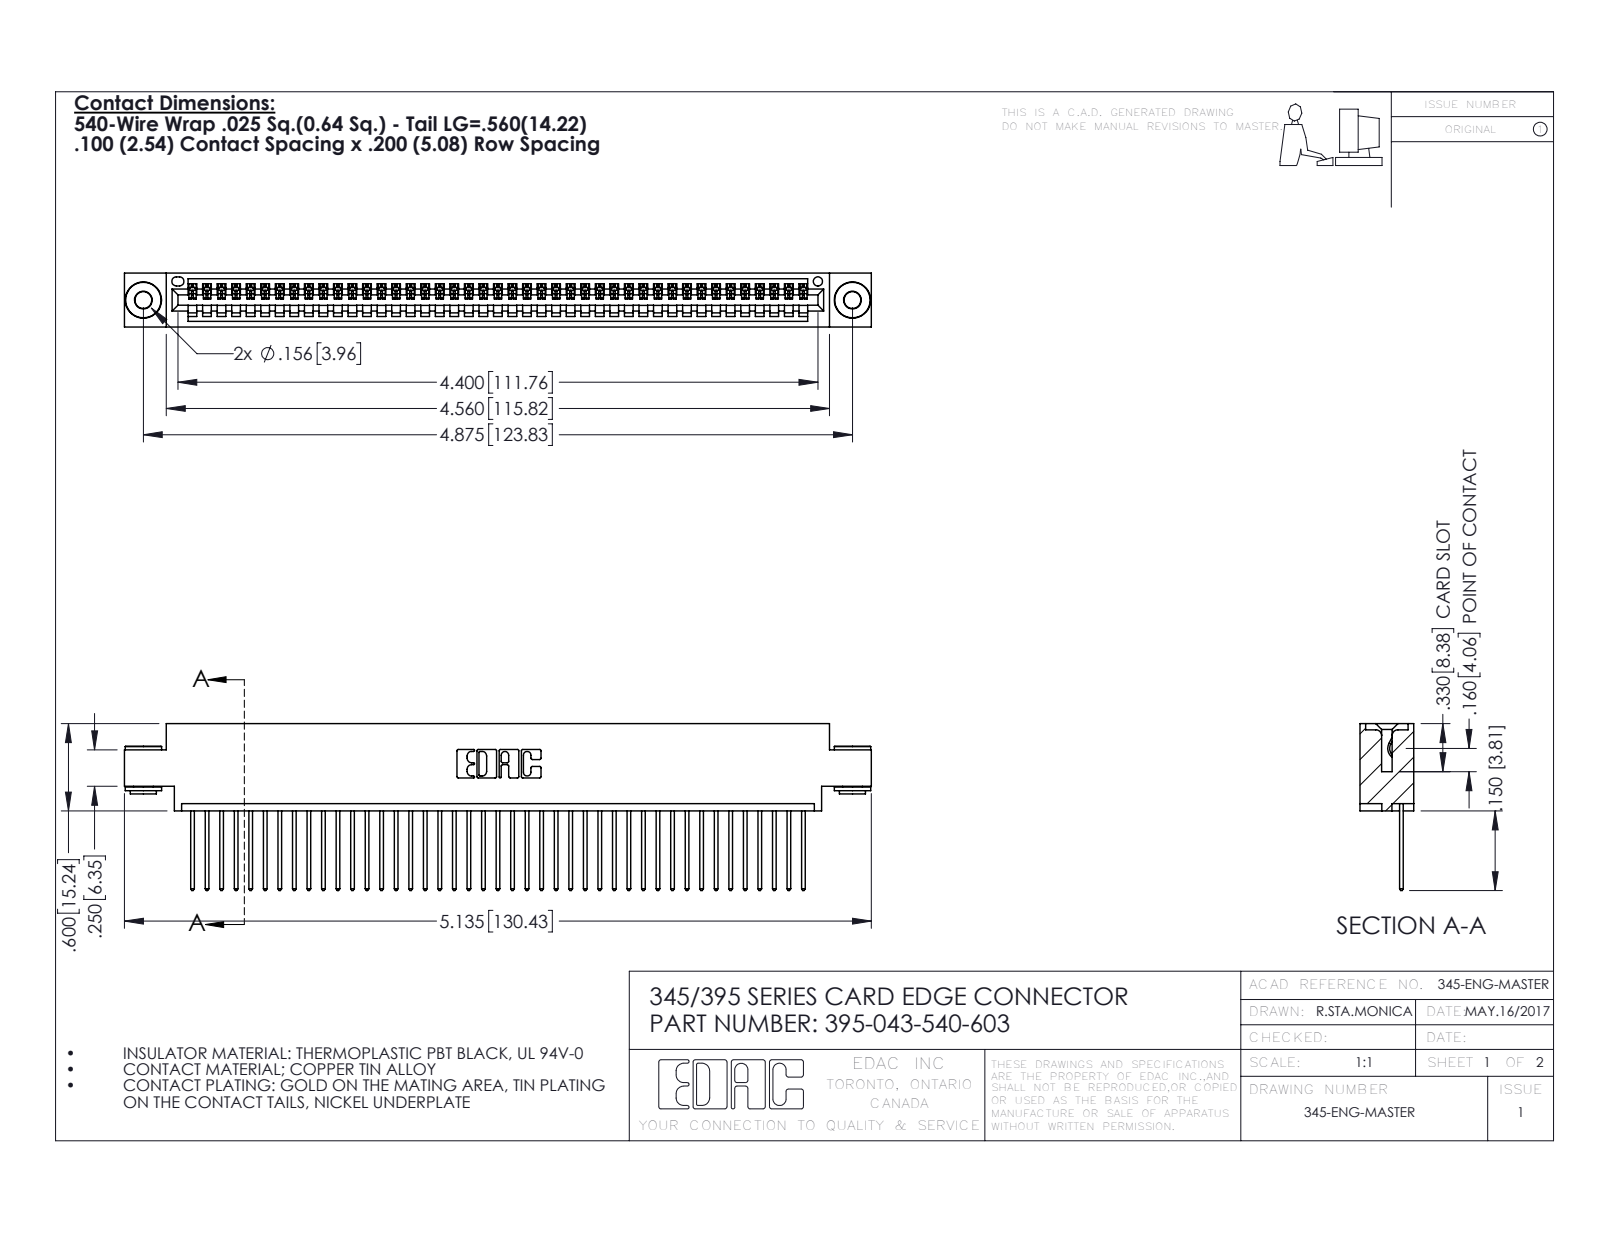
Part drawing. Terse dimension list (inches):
name: 395-043-540-603; 345-250-002_345-250-002-102; 345 Part_0.170 Offset - 0.156 Dia-TH; 345-292-001_345-293-140
written by: SolidWorks 2016 (CONFIG_CONTROL_DESIGN)
unit: in
bodies: 46 solids, 2662 faces (1814 planar, 840 cylindrical, 8 other)
size: 5.135 × 1.147 × 0.37
volume: 0.754 in³; area: 26.66 in²
holes: 2× ⌀0.116, 2× ⌀0.156, 1× ⌀0.064
bosses: 2× ⌀0.25, 2× ⌀0.18, 2× ⌀0.136
rounds: 86× R0.006, 86× R0.01, 22× R0.01, 6× R0.007, 6× R0.031, 3× R0.026, 2× R0.031, 2× R0.04
face distances: 0.072, 0.298, 0.37, 0.098, 0.272, 0.025, 0.2, 0.225, 0.175, 0.149
hole spacings: 0.27, 4.639, 4.875
